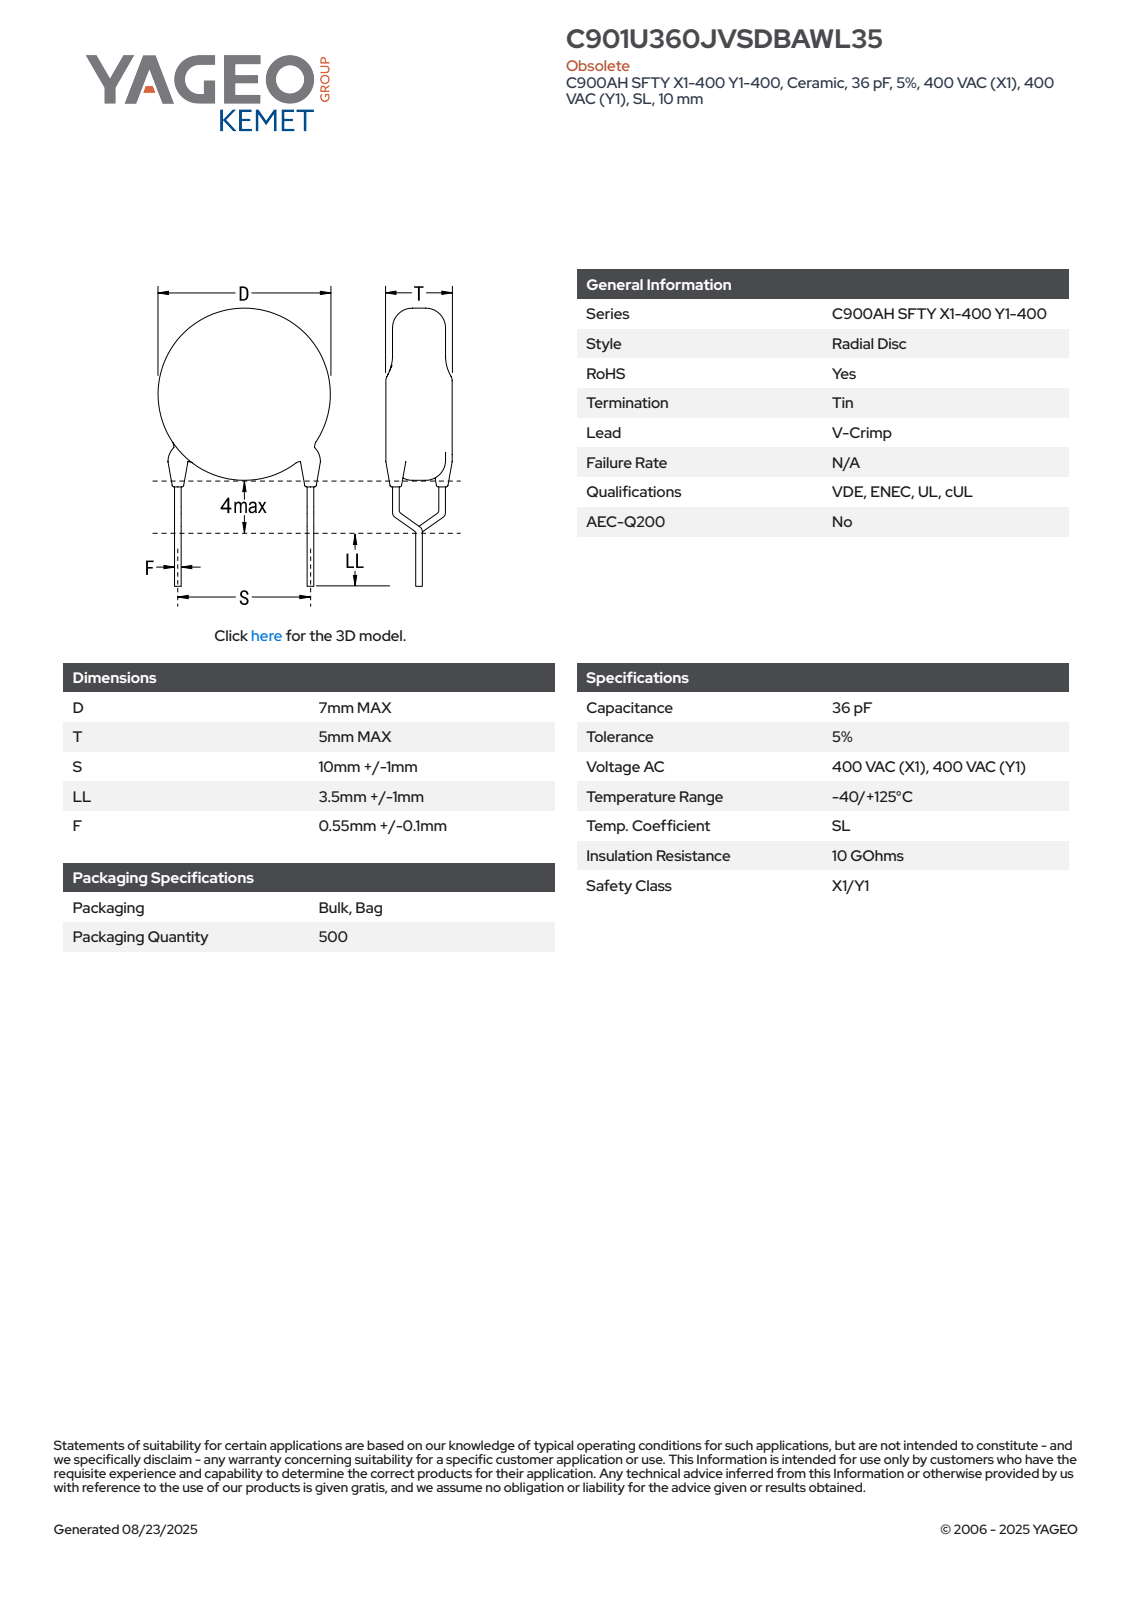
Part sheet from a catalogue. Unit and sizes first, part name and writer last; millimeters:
Units: millimetres
Overall size (bounding box): 15.3 × 10.65 × 5
Round bosses / shafts (diameter × count): ⌀0.65 ×6, ⌀7 ×1
Main face-to-face distances: 5, 7.4, 0.91, 12.25, 4.85, 11.34, 3.94, 3.71, 0.34, 1.87
Volume: 195 mm³ · Surface area: 225 mm²
Bodies: 5 solids, 93 faces (65 planar, 16 cylindrical, 12 other)
Part name (STEP PRODUCT): CCD_VCC900_D7T5S10LL4.5F0.65
STEP written by: SolidWorks 2014 (AUTOMOTIVE_DESIGN)
